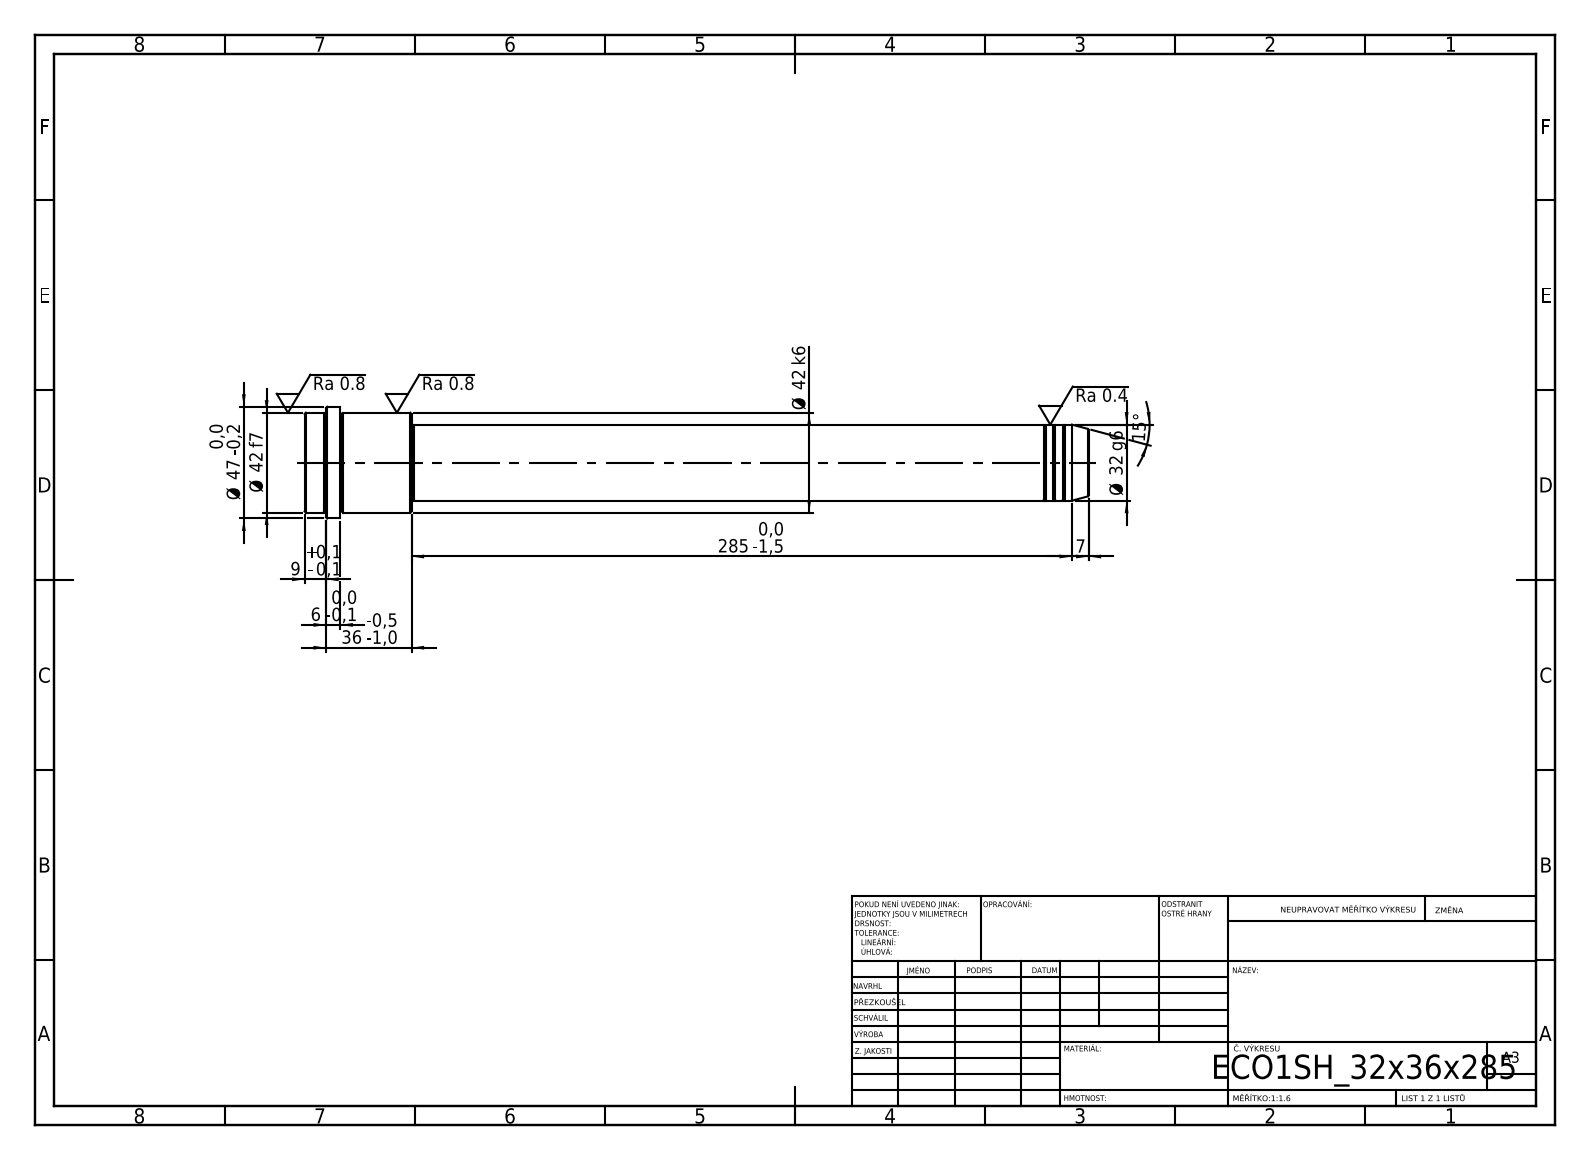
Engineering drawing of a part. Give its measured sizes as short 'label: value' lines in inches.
written by: SolidWorks 2019 (CONFIG_CONTROL_DESIGN)
unit: in
bodies: 1 solid, 52 faces (6 planar, 16 cylindrical, 30 other)
size: 12.992 × 1.85 × 1.85
volume: 17.86 in³; area: 59.26 in²
bosses: 1× ⌀1.85, 1× ⌀1.654, 1× ⌀1.26, 1× ⌀1.22
face distances: 12.992, 11.22, 1.772, 12.402, 1.181, 0.591, 12.638, 1.417, 0.236, 0.354
